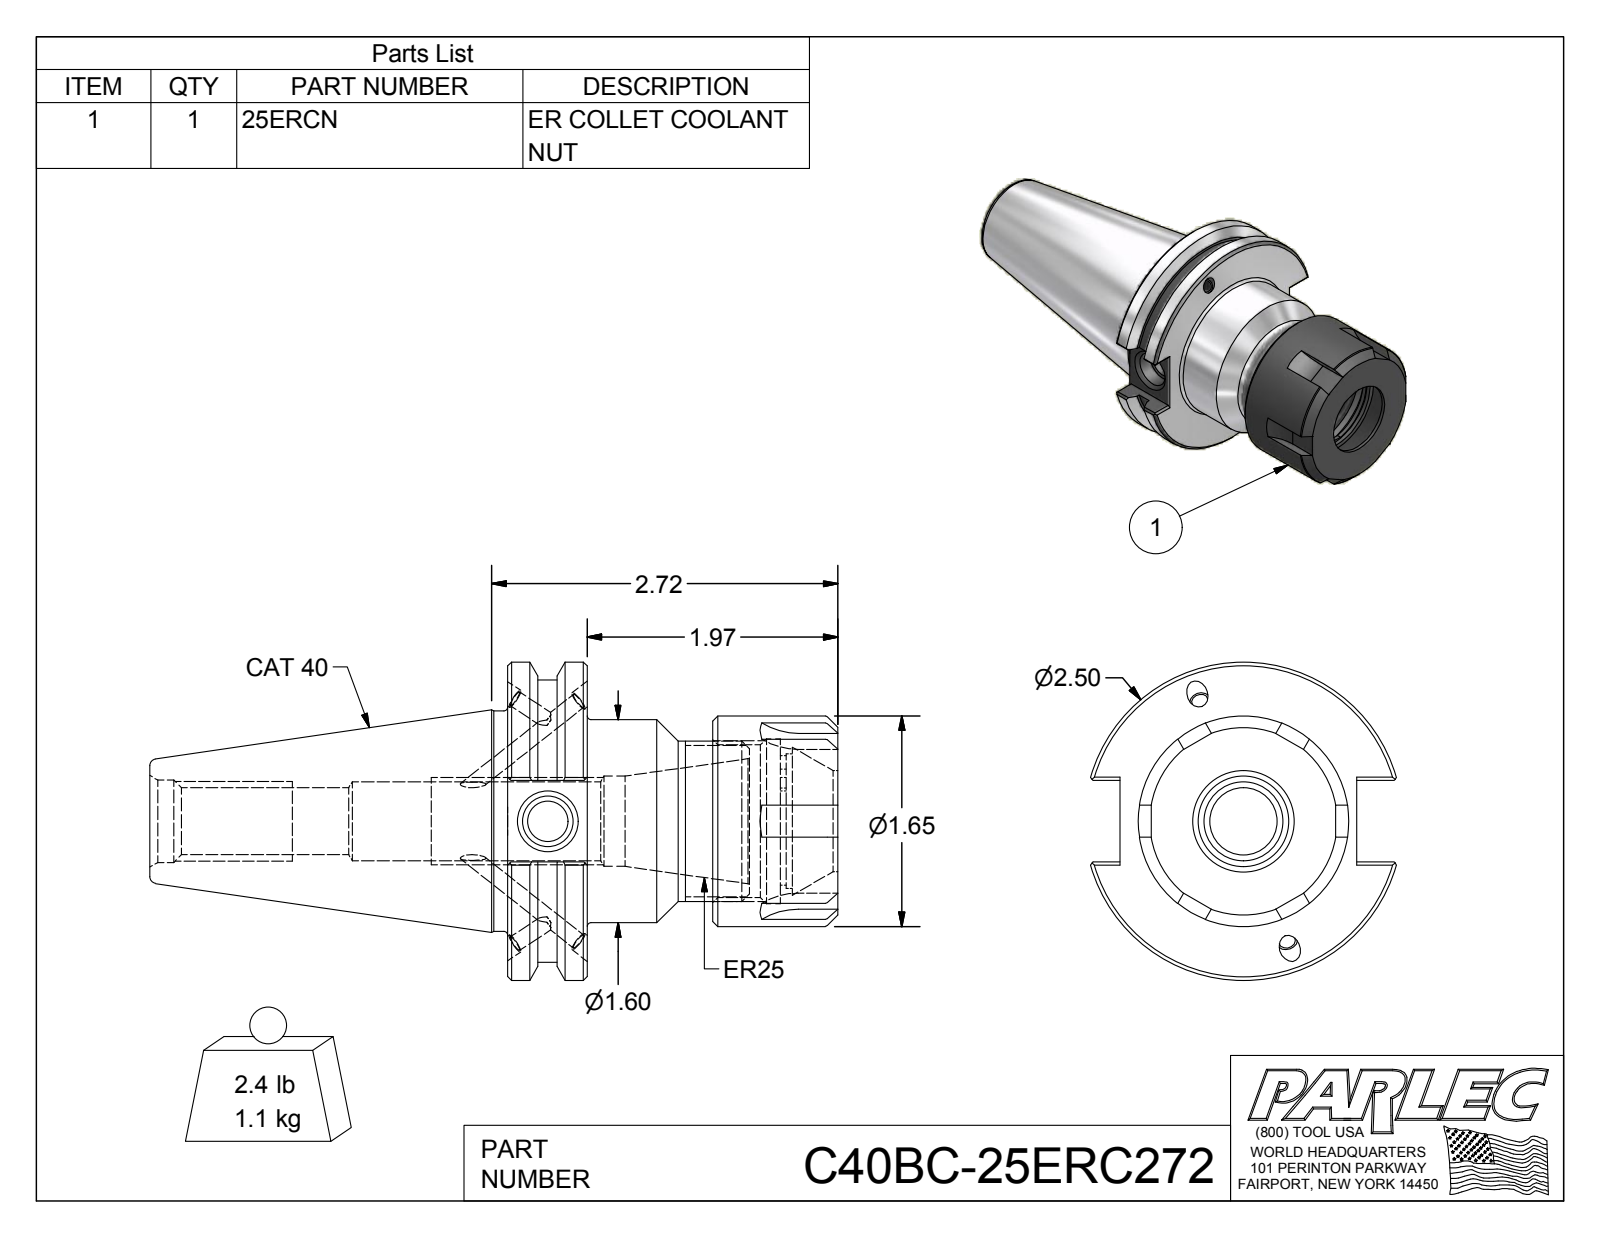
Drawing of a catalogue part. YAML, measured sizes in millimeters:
part_name: "C40BCB-25ER2-1; 029-965; 25ERCN; C40BC-25ERC272"
step_written_by: "Autodesk Inventor 2016 (AUTOMOTIVE_DESIGN)"
units: millimeters
bodies: {solids: 6, faces: 209, planar: 103, cylindrical: 51, other: 55}
overall_size: [137.35, 63.5, 61.05]
volume: 137337
surface_area: 34641
round_holes:
  - {diameter: 3.3, count: 4}
  - {diameter: 4.1, count: 4}
  - {diameter: 8, count: 1}
  - {diameter: 10.05, count: 1}
  - {diameter: 13.39, count: 1}
  - {diameter: 15.75, count: 1}
  - {diameter: 16.46, count: 1}
  - {diameter: 18.03, count: 1}
  - {diameter: 20.18, count: 1}
  - {diameter: 26.86, count: 1}
  - {diameter: 30.5, count: 1}
  - {diameter: 32.88, count: 1}
round_bosses_or_shafts:
  - {diameter: 4.2, count: 4}
  - {diameter: 4, count: 4}
  - {diameter: 63.5, count: 1}
  - {diameter: 56.36, count: 1}
  - {diameter: 43.94, count: 1}
  - {diameter: 42, count: 1}
  - {diameter: 40.51, count: 1}
  - {diameter: 32, count: 1}
partial_cylinders:
  - {radius: 12.7, count: 6}
  - {radius: 12, count: 1}
  - {radius: 13.07, count: 1}
face_to_face_distances: [15.88, 65.92, 50.04, 40.92, 25.04, 25, 54.42, 38.54, 13.5, 11.5]
